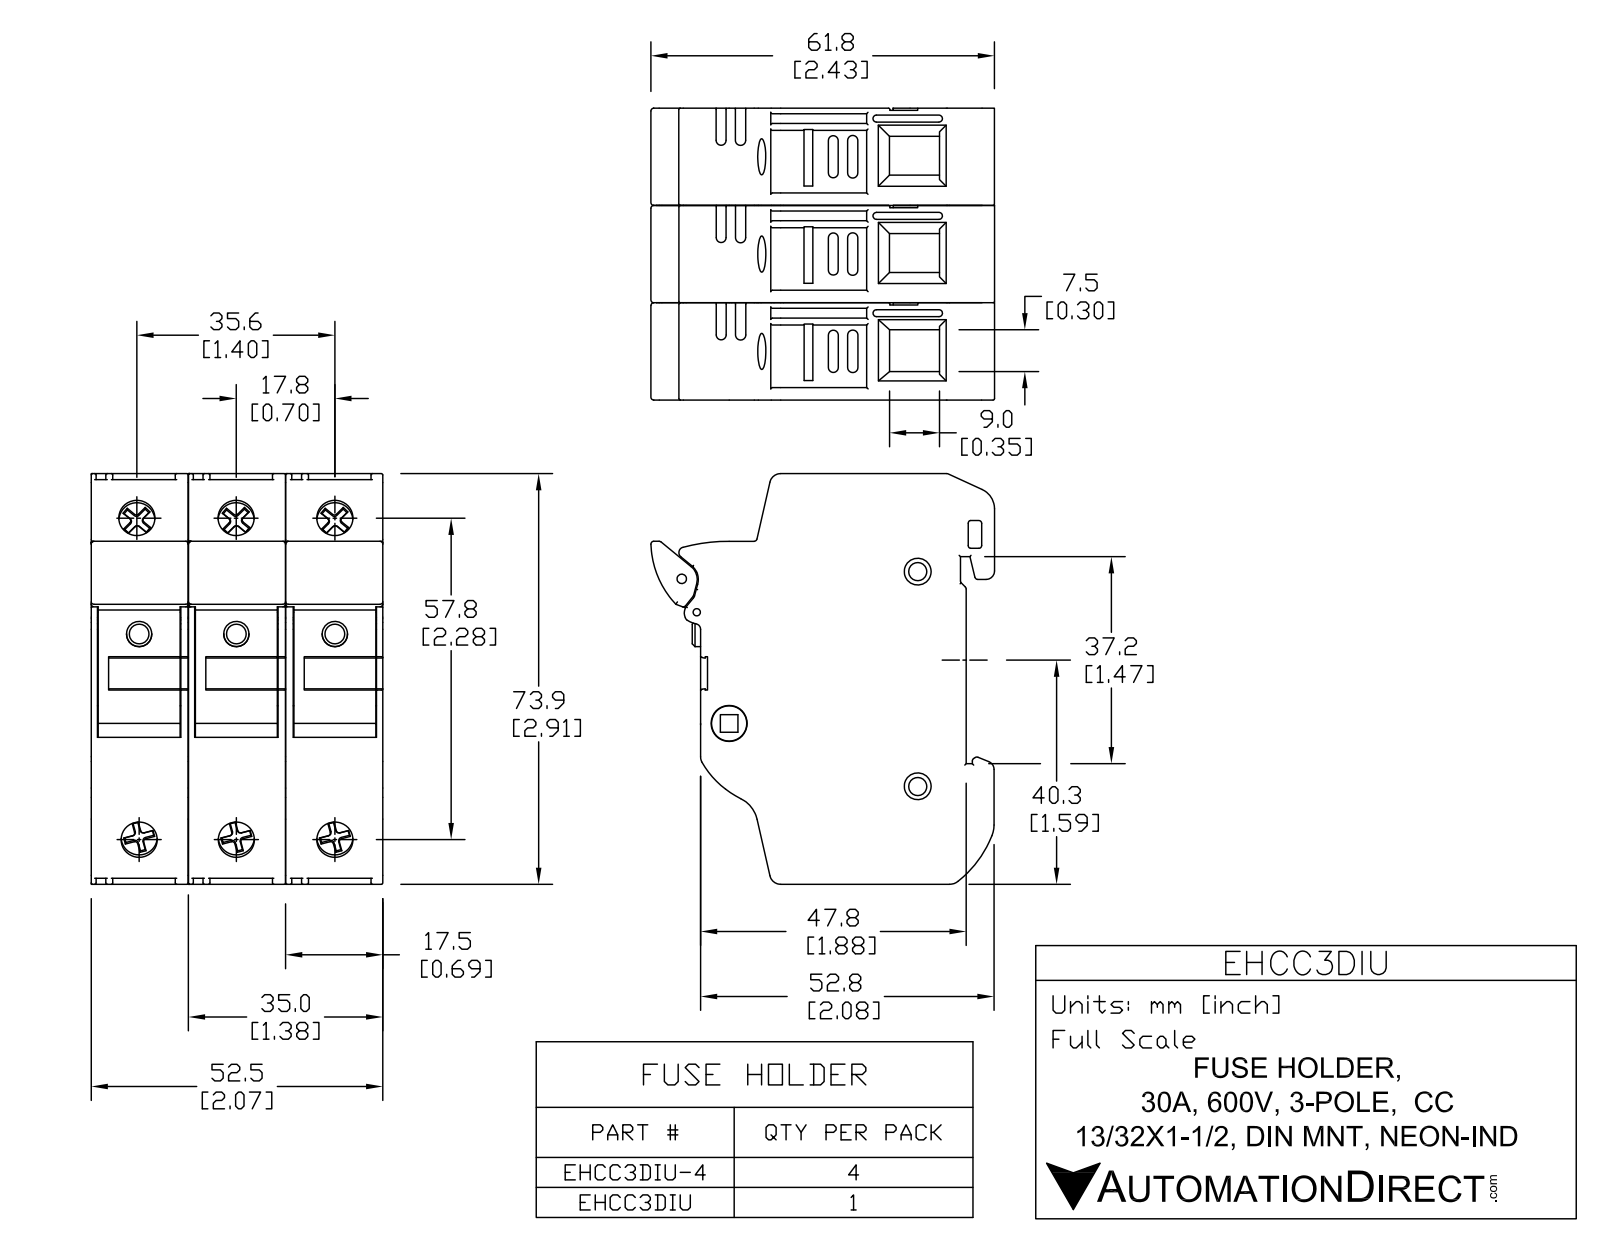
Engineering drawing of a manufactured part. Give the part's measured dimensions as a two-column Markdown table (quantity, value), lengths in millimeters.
| quantity | value |
| --- | --- |
| part name | EHCC3DIU |
| STEP written by | SolidWorks 2011 (AUTOMOTIVE_DESIGN) |
| units | millimeters |
| bodies | 2 solids, 1583 faces (751 planar, 510 cylindrical, 322 other) |
| overall size | 73.88 × 61.82 × 52.52 |
| volume | 158 267 mm³ |
| surface area | 48 387 mm² |
| round holes (diameter × count) | 6.5 × 6, 3.25 × 2, 4.83 × 2, 1.3 × 1, 1.7 × 1, 6.48 × 1 |
| round bosses / shafts (diameter × count) | 4.55 × 3, 6.35 × 1 |
| partial cylindrical surfaces (radius × count) | 0.25 × 141, 0.62 × 12, 0.5 × 11, 2 × 10, 0.51 × 9, 0.89 × 9, 0.92 × 9, 0.75 × 7 |
| main face-to-face distances | 17.5, 35, 52.5, 1.25, 1.58, 16.25, 27.51, 29.09, 22.94, 24.71 |
| hole center spacings | 17.51, 35.02, 6.58, 20.83, 27.36, 35.77, 35.79, 38.61 |
